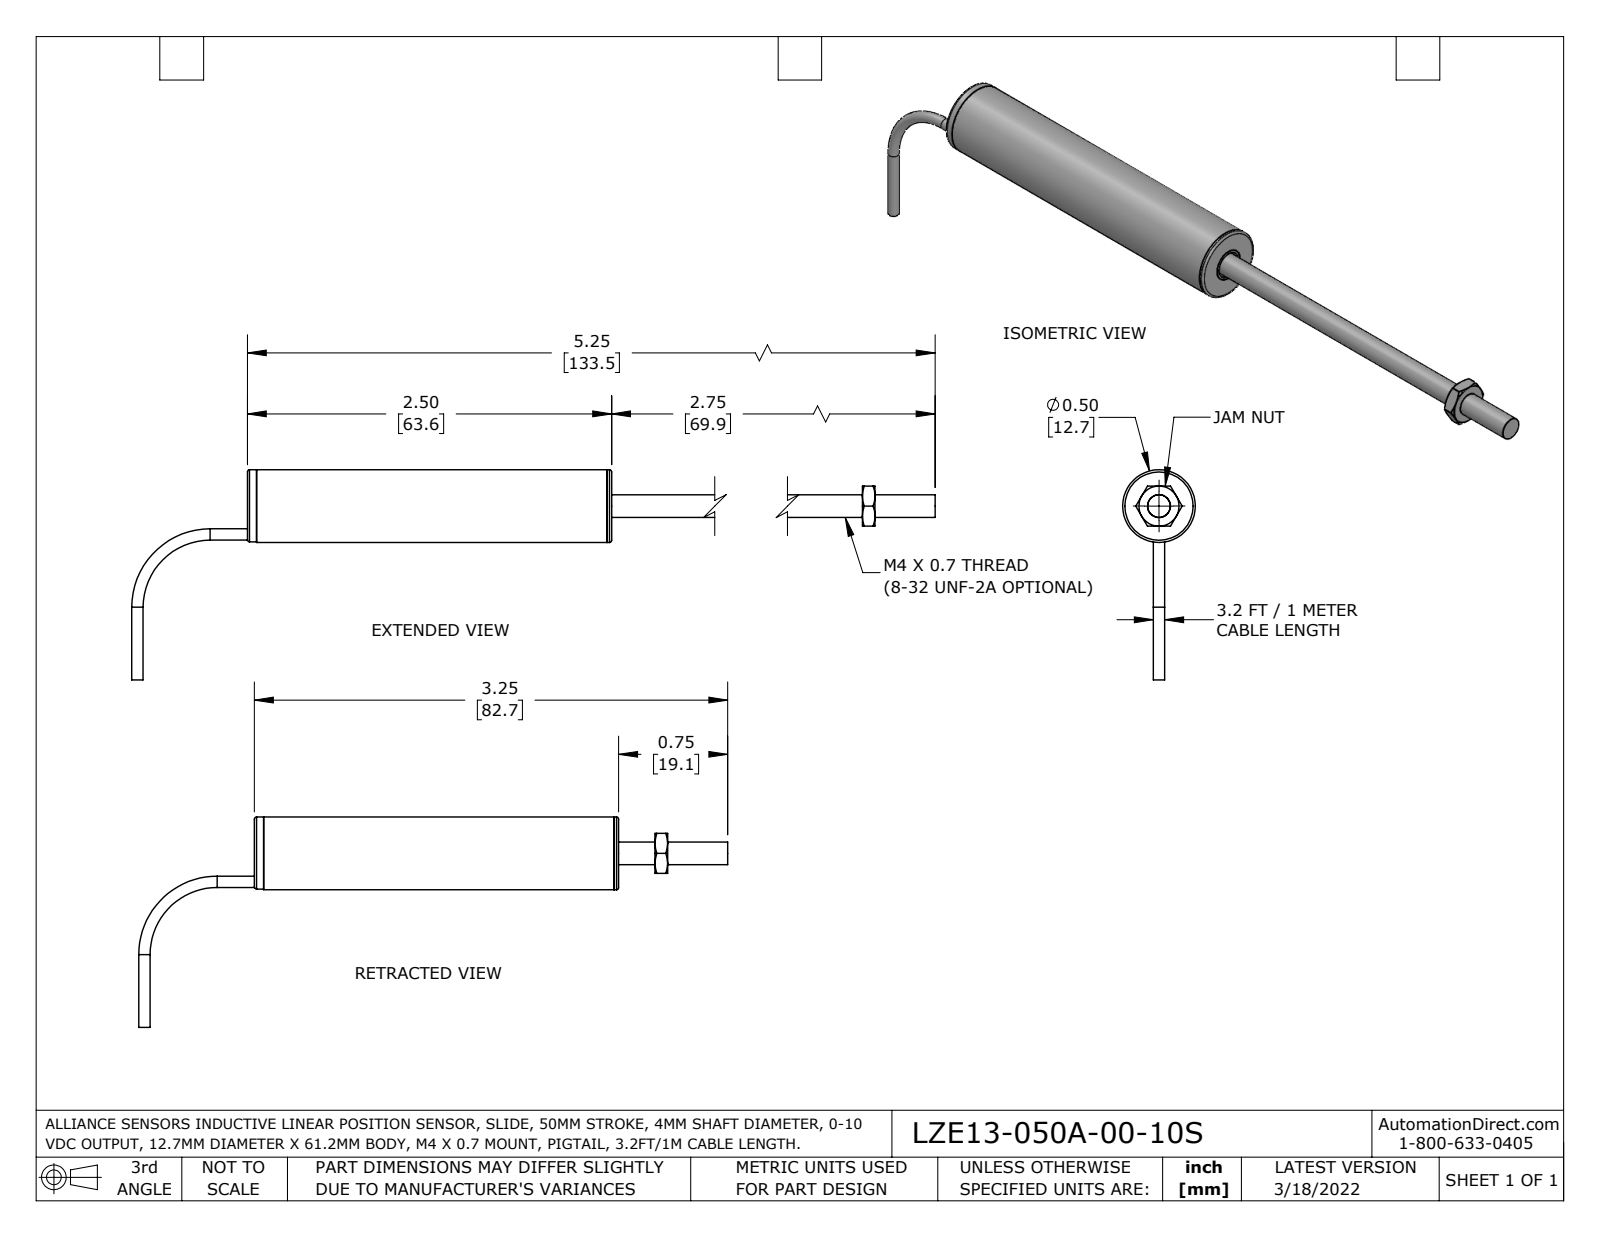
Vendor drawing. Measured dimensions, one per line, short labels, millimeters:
name: 3100-0300_90710A035; 5500-0029; LZE13-050A-00-10S; 3120-0034-XX-Z_3120-0034-02-Z (+6 more)
written by: SolidWorks 2021 (AUTOMOTIVE_DESIGN)
unit: mm
bodies: 9 solids, 98 faces (32 planar, 38 cylindrical, 28 other)
size: 153.6 × 36.7 × 12.7
volume: 3 360 mm³; area: 9 510 mm²
holes: 1× ⌀2, 1× ⌀4, 1× ⌀4.7, 1× ⌀5.7
bosses: 1× ⌀12.7, 1× ⌀11.9, 1× ⌀5.6, 1× ⌀4, 1× ⌀2.5, 1× ⌀2
rounds: 1× R1.2
face distances: 2, 1.6, 7, 2.4, 63.6, 62, 61.2, 59.6, 0.8, 57.2
hole spacings: 5
